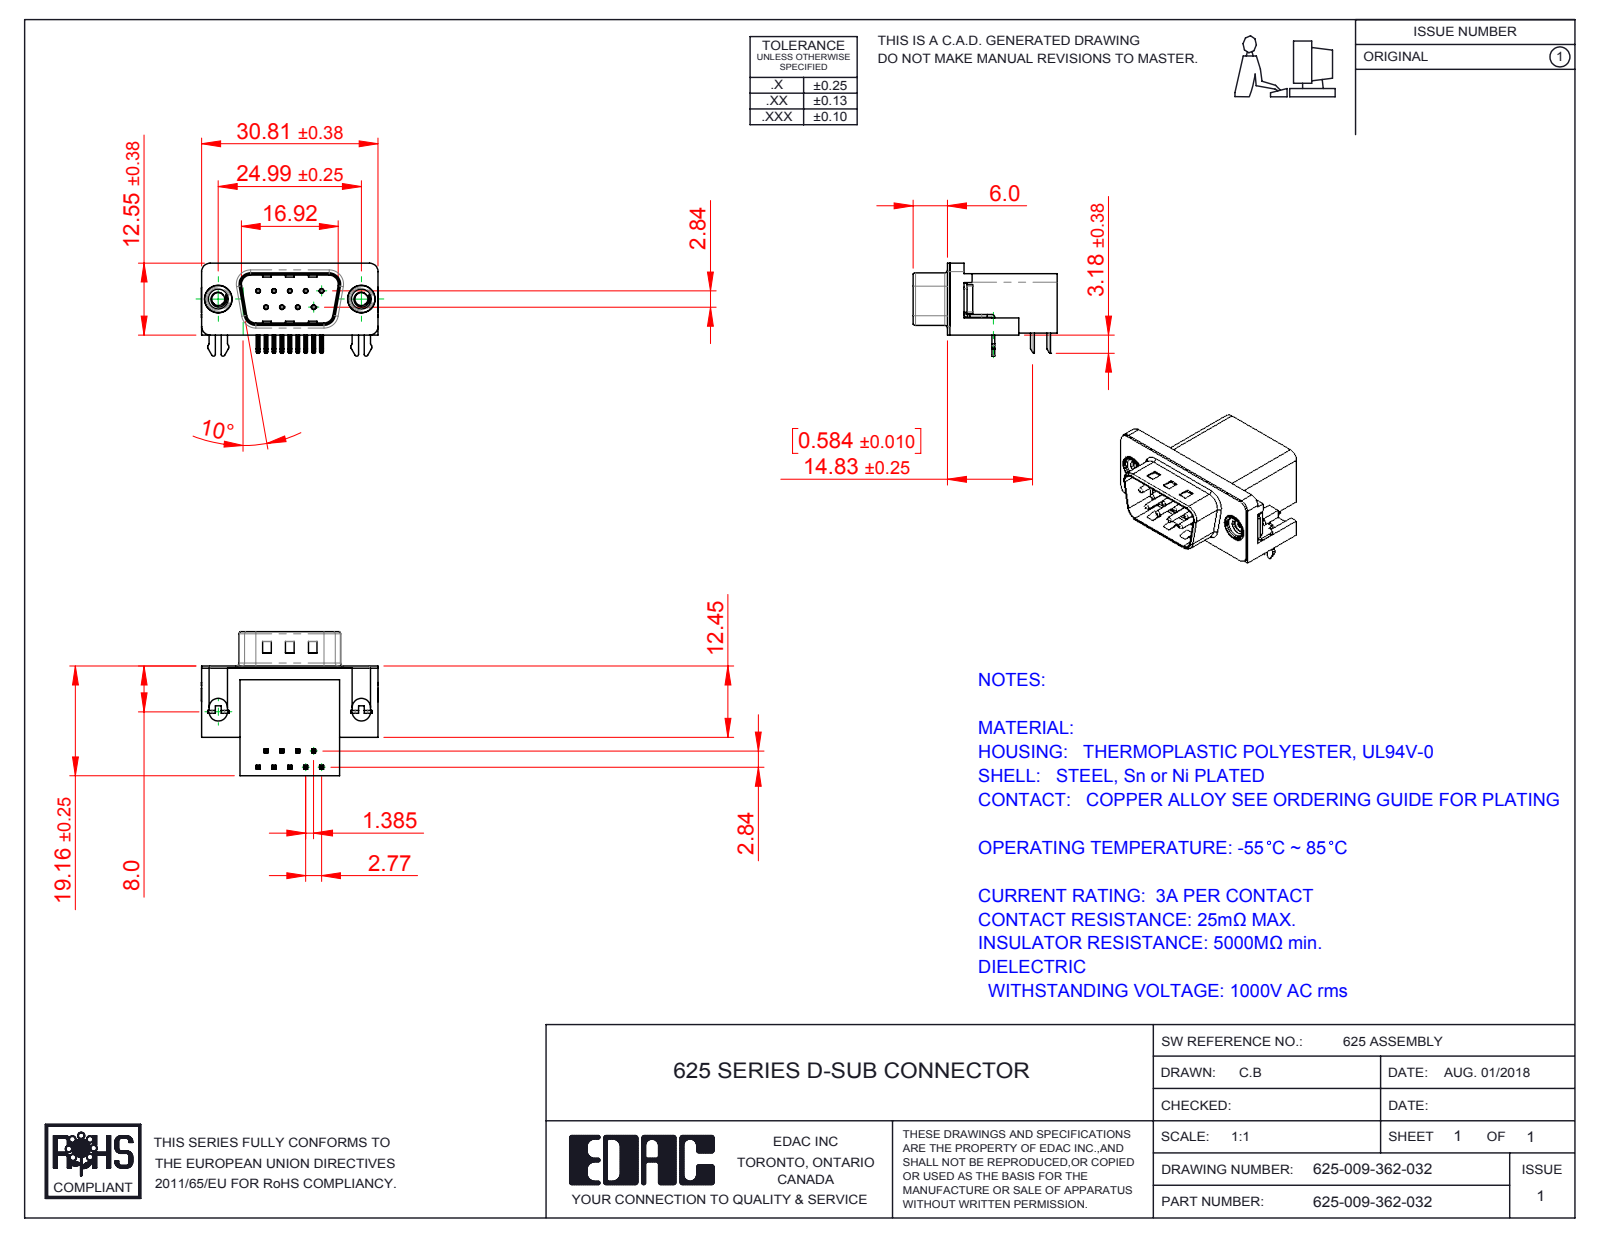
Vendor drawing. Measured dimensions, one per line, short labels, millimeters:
name: 625 Shell_9 Socket; 625 Contact Top; 625-009-362-032; 625 Contact Bottom (+3 more)
written by: SolidWorks 2016 (CONFIG_CONTROL_DESIGN)
unit: mm
bodies: 15 solids, 1033 faces (605 planar, 325 cylindrical, 103 other)
size: 30.89 × 25.16 × 16.25
volume: 4 476 mm³; area: 4 957 mm²
holes: 9× ⌀0.35, 9× ⌀0.8, 2× ⌀2.26, 2× ⌀4, 2× ⌀4.8, 2× ⌀5
bosses: 9× ⌀0.75, 2× ⌀4.9, 2× ⌀4.75, 2× ⌀3.9
rounds: 44× R0.25, 18× R0.12, 16× R1, 14× R0.5, 8× R1.5, 8× R1.6, 4× R0.32, 4× R0.9
face distances: 0.4, 10.34, 18.76, 19.16, 16.26, 2.5, 2.9, 0.35, 10.69, 0.5
hole spacings: 3.16, 2.77, 5.54, 5.03, 5.04, 8.31, 7.48, 7.49
